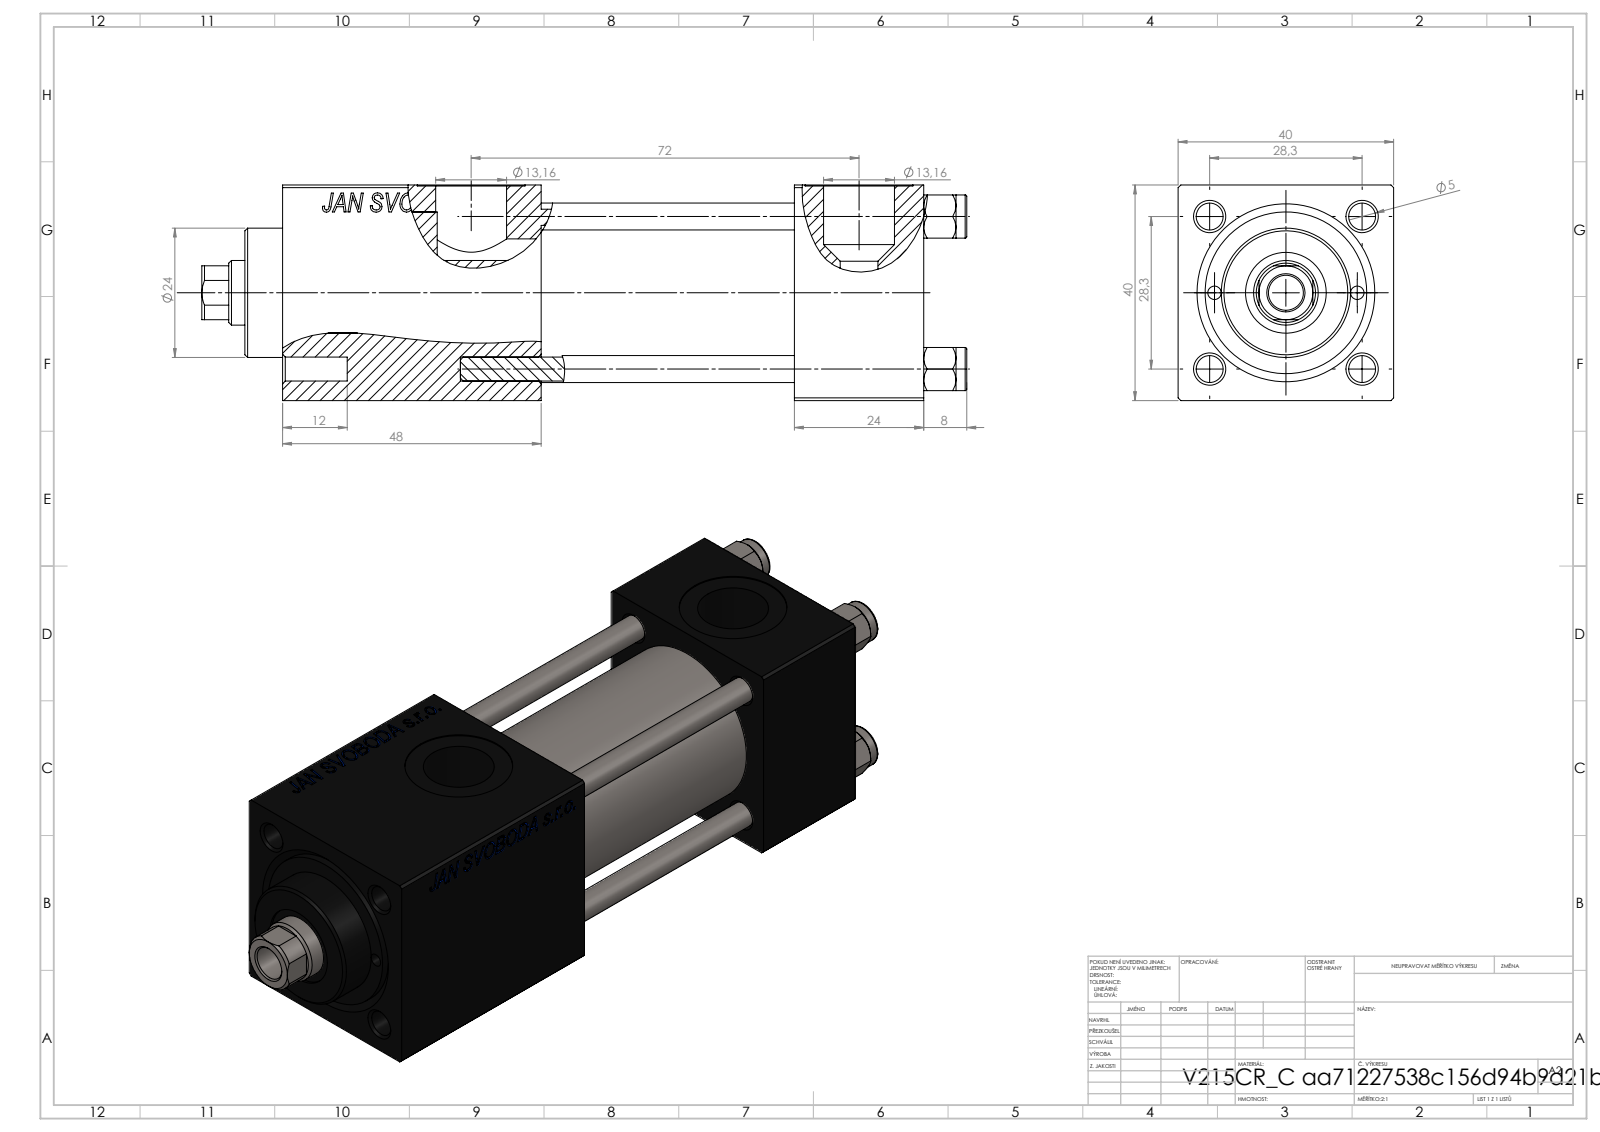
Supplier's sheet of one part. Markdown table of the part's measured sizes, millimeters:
| quantity | value |
| --- | --- |
| part name | V215CR_VCP_C; V215CR_C_Body; V215_VC_A; NUT_M5_C (+1 more) |
| STEP written by | SolidWorks 2019 (CONFIG_CONTROL_DESIGN) |
| units | millimeters |
| bodies | 11 solids, 1154 faces (527 planar, 91 cylindrical, 536 other) |
| overall size | 142 × 40 × 40 |
| volume | 142 260 mm³ |
| surface area | 54 521 mm² |
| round holes (diameter × count) | 5 × 4, 20 × 3, 2.5 × 2, 7 × 2, 13.16 × 2, 6.5 × 1, 12 × 1, 15 × 1, 25 × 1, 30 × 1 |
| round bosses / shafts (diameter × count) | 8 × 4, 31 × 1, 24 × 1 |
| partial cylindrical surfaces (radius × count) | 5.5 × 1 |
| main face-to-face distances | 40, 24, 90.3, 66.3, 48, 71, 47, 19.3, 119, 95 |
| hole center spacings | 14.18, 20.01, 28.3, 30.84, 13.25, 40.02, 26.5, 72 |
